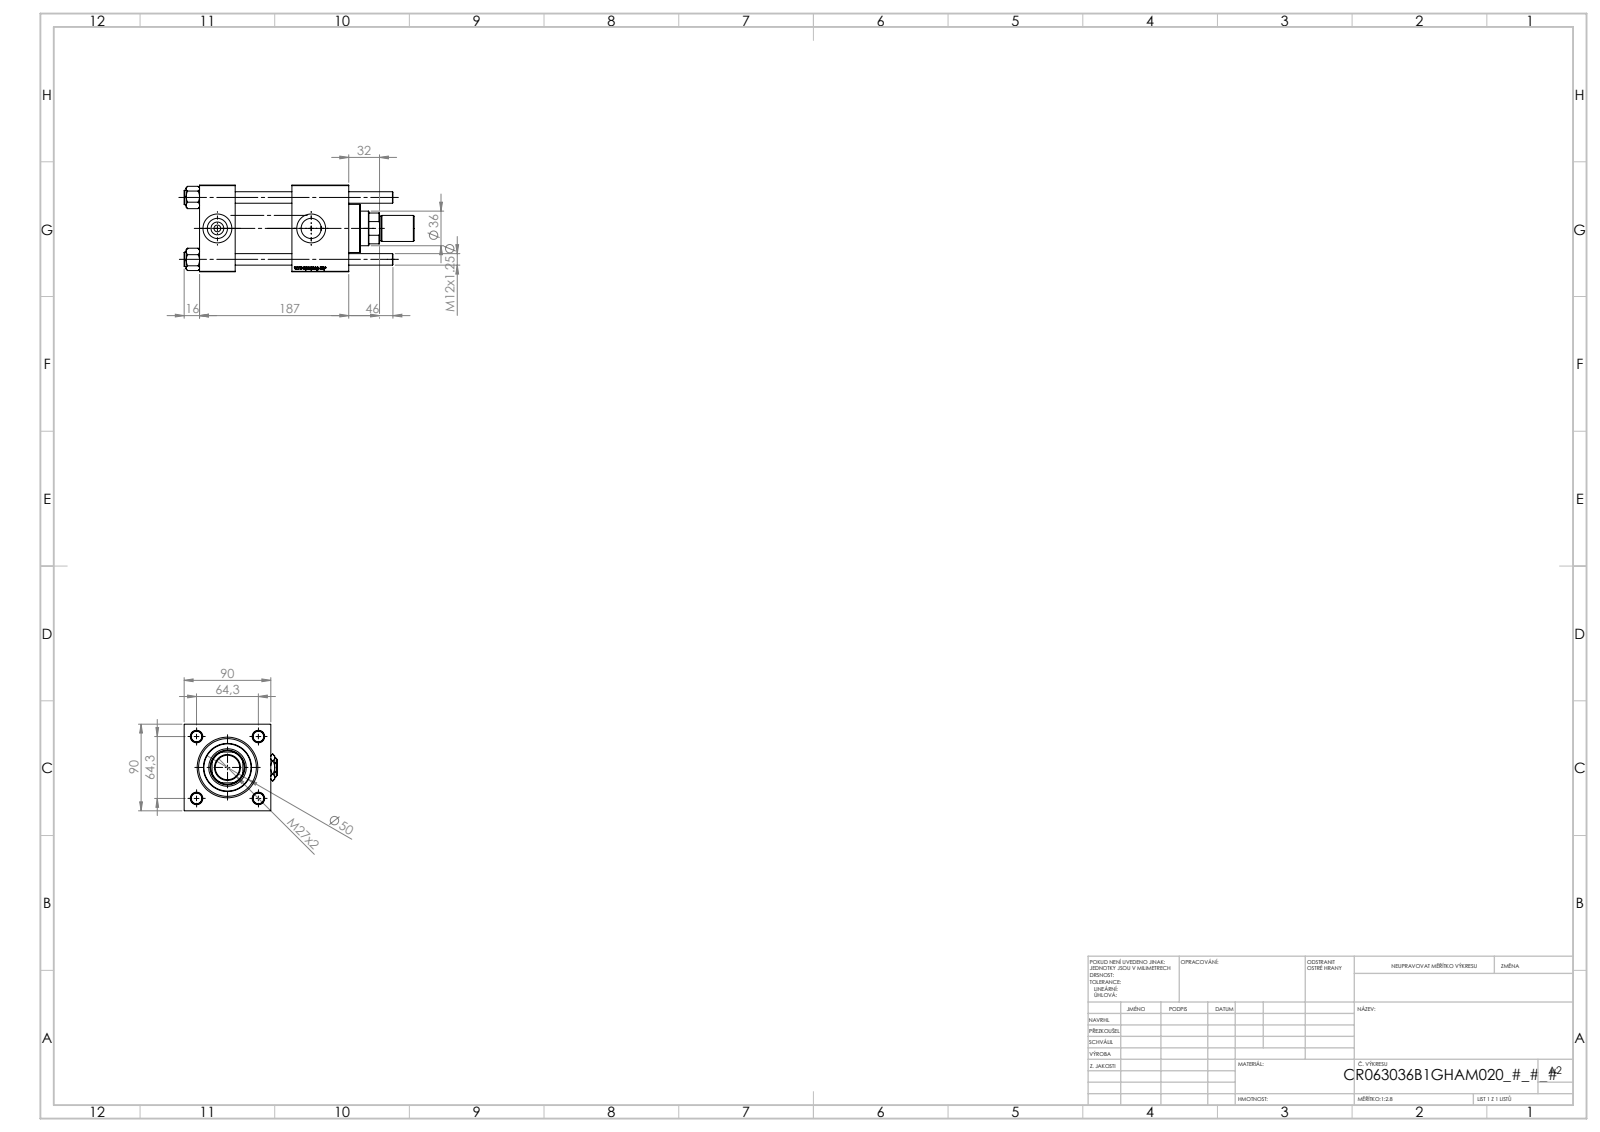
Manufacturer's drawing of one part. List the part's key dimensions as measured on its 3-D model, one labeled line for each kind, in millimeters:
Part name (STEP PRODUCT): V215CR_B-1; V215CR_B_TYCINKA; Zatka_pro_OIL_PORT; ROD_END_AH (+3 more)
STEP written by: SolidWorks 2019 (CONFIG_CONTROL_DESIGN)
Units: millimetres
Bodies: 13 solids, 1219 faces (459 planar, 86 cylindrical, 674 other)
Overall size (bounding box): 239 × 97 × 90
Volume: 1 018 000 mm³ · Surface area: 206 507 mm²
Round holes (diameter × count): ⌀12 ×4, ⌀7 ×2, ⌀20.96 ×2, ⌀30 ×2, ⌀25.5 ×1, ⌀36 ×1, ⌀39 ×1, ⌀50 ×1, ⌀60 ×1, ⌀63 ×1
Round bosses / shafts (diameter × count): ⌀15 ×4, ⌀69 ×1, ⌀27 ×1, ⌀25 ×1
Partial cylindrical surfaces — rounded edges, fillets, slot ends (radius × count): R17.5 ×1
Main face-to-face distances: 90, 59, 37, 118, 155, 96, 20, 126.3, 89.3, 30.3
Hole centre spacings: 45.47, 64.3, 90.93, 97.5
